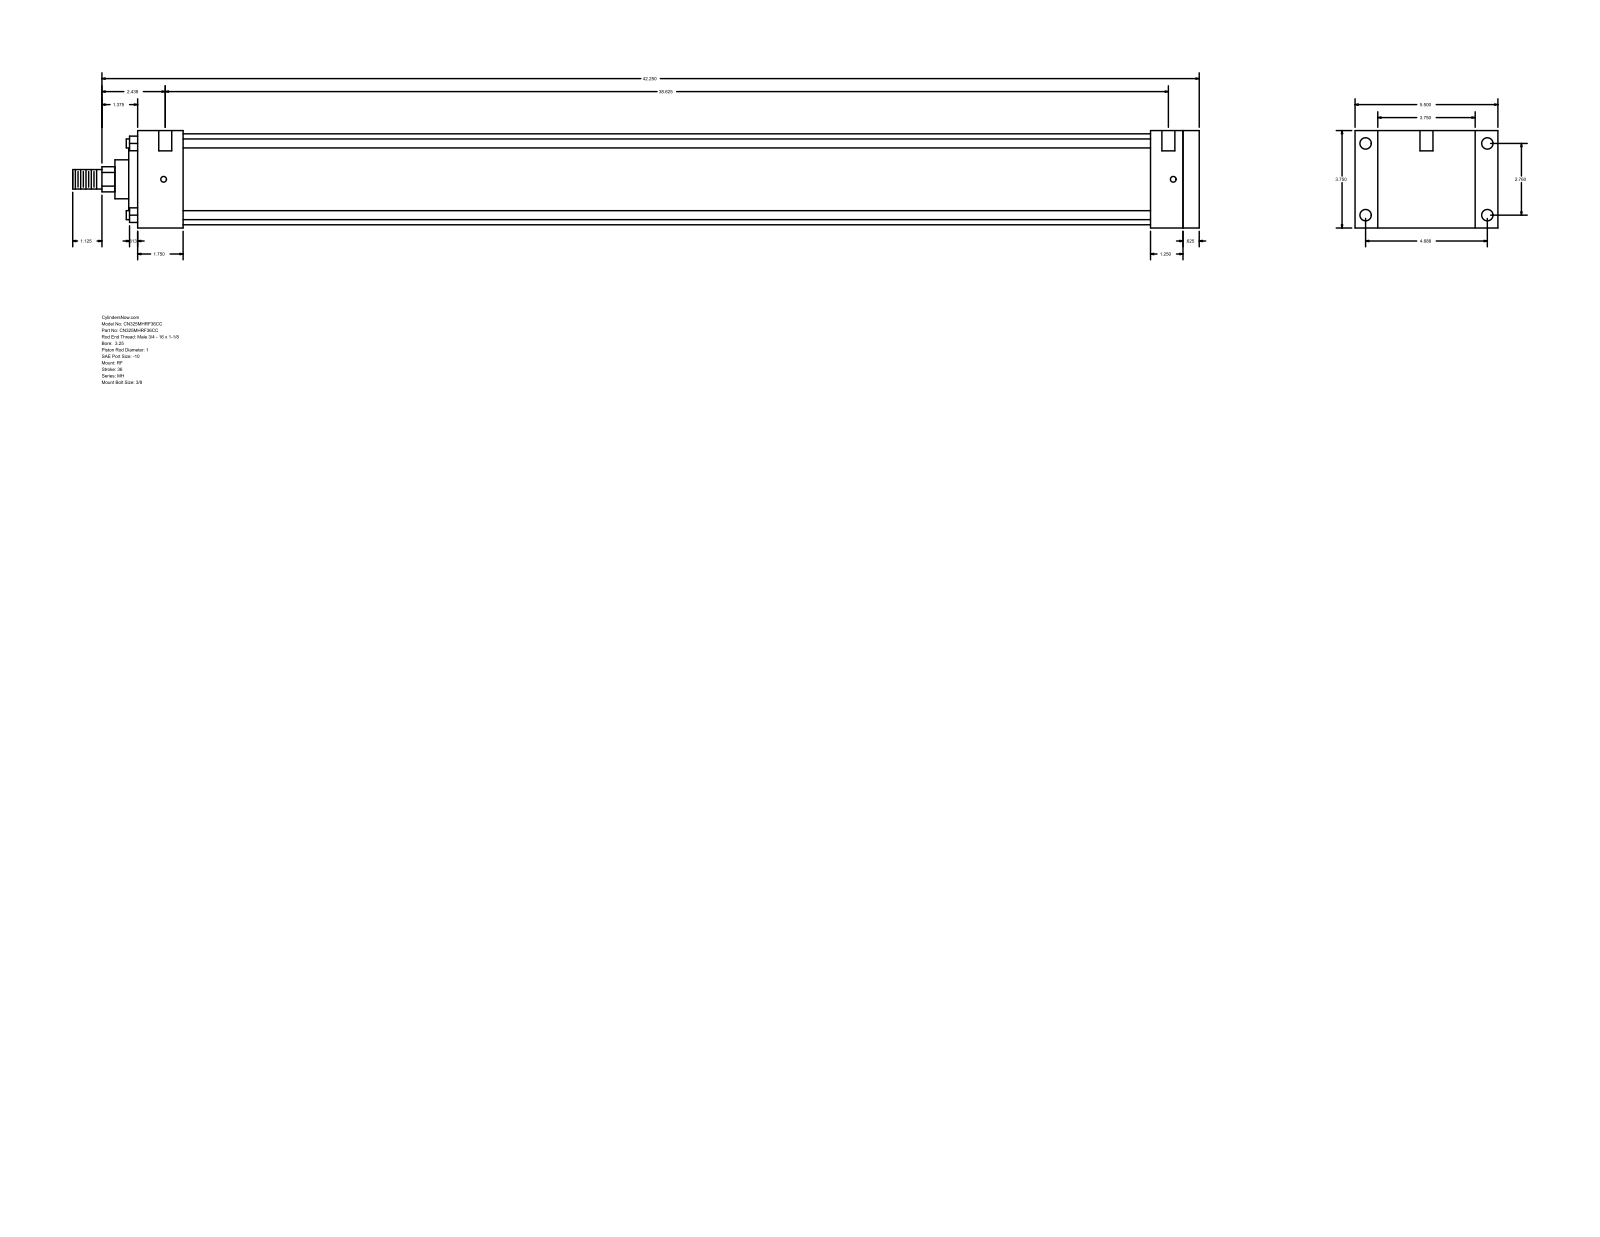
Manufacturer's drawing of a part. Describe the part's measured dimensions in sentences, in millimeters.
The part is named "MH_RF__0325_1". Its 3-D file was written by "GSSL Pune (CONFIG_CONTROL_DESIGN)". It is 0 solids with 94 faces: 65 planar, 29 cylindrical and 0 other. Overall it measures 1101.72 by 139.7 by 95.25 millimeters. Round holes: 4 of diameter 5.56, 4 of diameter 11.13, 2 of diameter 12.7. Round bosses or shafts: 4 of diameter 8.76, 1 of diameter 88.9, 1 of diameter 60.33, 1 of diameter 38.1, 1 of diameter 25.4, 1 of diameter 19.05. Partial cylindrical surfaces (rounded edges, fillets, slot ends): 1 of radius 12.29. The main face-to-face distances are 95.24, 1038.23, 1022.36, 15.87, 22.23, 117.47, 44.46, 977.9, 993.77, 990.61. The hole center spacings are 70.1, 119.06, 138.16, 987.42, 1.58, 4.76, 981.08, 982.66.
